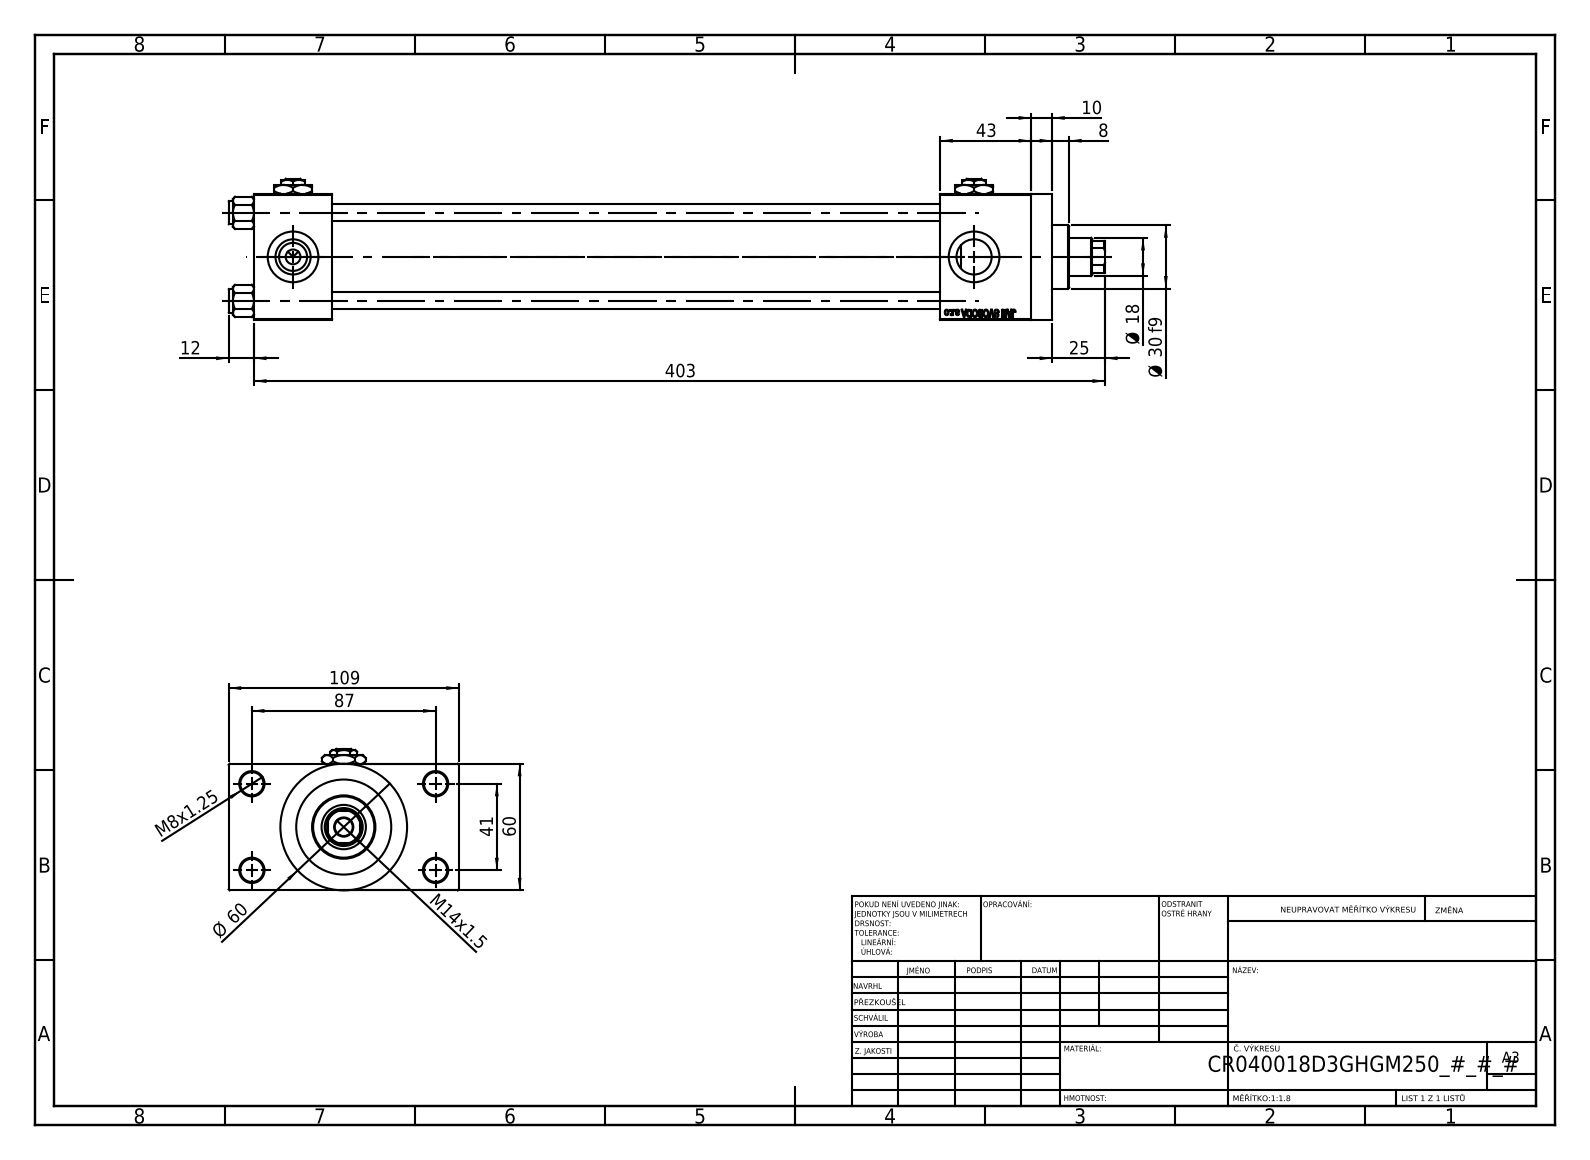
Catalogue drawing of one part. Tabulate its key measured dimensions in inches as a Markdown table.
| quantity | value |
| --- | --- |
| part name | V215_VC_A; V215CR_VCP_D; V215CR_D_Body; NUT_M5_D (+2 more) |
| STEP written by | SolidWorks 2019 (CONFIG_CONTROL_DESIGN) |
| units | inches |
| bodies | 13 solids, 1205 faces (546 planar, 99 cylindrical, 560 other) |
| overall size | 16.339 × 4.291 × 2.638 |
| volume | 43.22 in³ |
| surface area | 346.4 in² |
| round holes (diameter × count) | 0.315 × 4, 0.433 × 4, 0.656 × 4, 0.945 × 4, 0.276 × 3, 0.335 × 1, 0.709 × 1, 0.827 × 1, 1.22 × 1, 1.575 × 1, 1.772 × 1 |
| round bosses / shafts (diameter × count) | 0.433 × 4, 2.362 × 1, 1.811 × 1, 1.181 × 1 |
| partial cylindrical surfaces (radius × count) | 0.335 × 1 |
| main face-to-face distances | 2.362, 11.339, 0.965, 3.327, 1.457, 12.795, 1.693, 14.488, 13.031, 0.394 |
| hole center spacings | 0.892, 1.161, 1.642, 1.856, 1.893, 2.533, 3.011, 1.614 |
